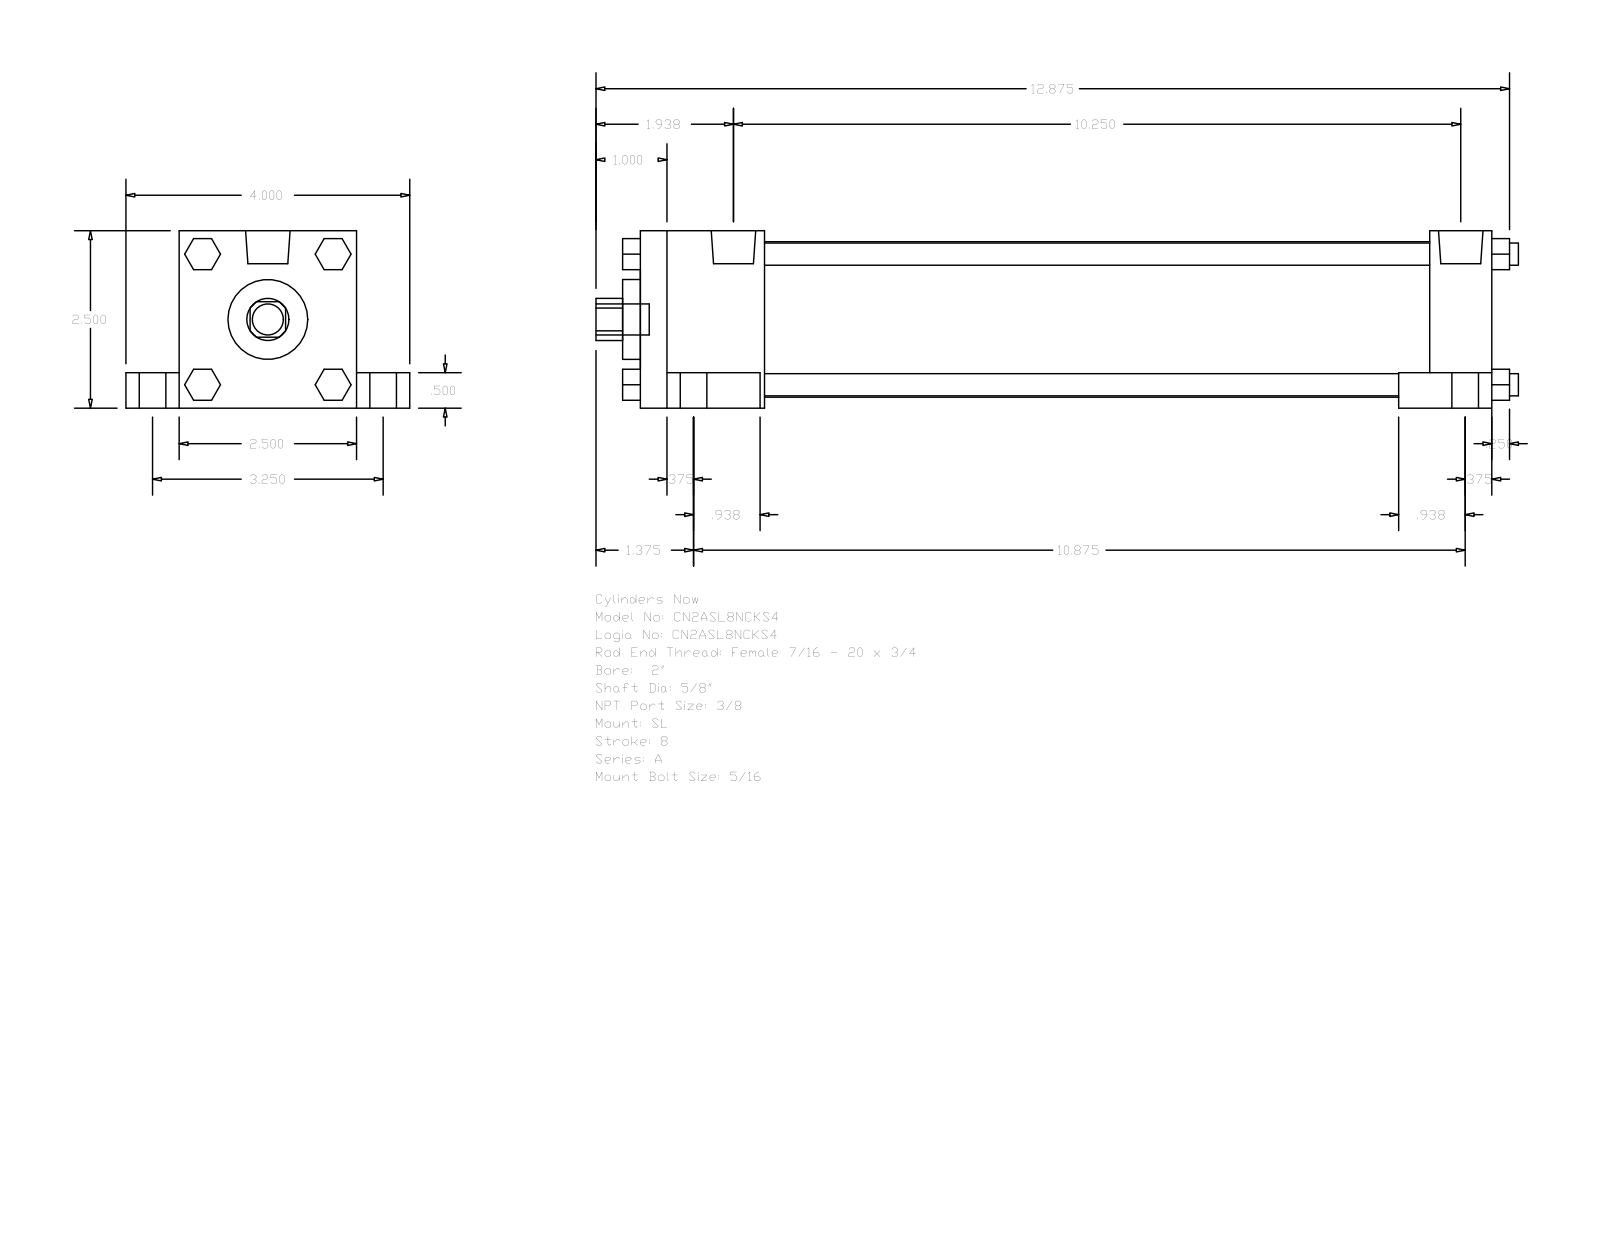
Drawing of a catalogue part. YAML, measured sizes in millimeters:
part_name: "A_SL__0200_0.625"
step_written_by: "GSSL Pune (CONFIG_CONTROL_DESIGN)"
units: millimeters
bodies: {solids: 0, faces: 148, planar: 112, cylindrical: 36, other: 0}
overall_size: [330.2, 101.6, 63.5]
round_holes:
  - {diameter: 15.88, count: 1}
  - {diameter: 28.57, count: 1}
  - {diameter: 55.63, count: 1}
round_bosses_or_shafts:
  - {diameter: 15.88, count: 4}
  - {diameter: 9.53, count: 4}
  - {diameter: 7.94, count: 4}
  - {diameter: 5.56, count: 4}
  - {diameter: 15.93, count: 2}
  - {diameter: 11.11, count: 1}
partial_cylinders:
  - {radius: 7.54, count: 1}
face_to_face_distances: [63.5, 304.8, 50.8, 12.7, 19.05, 82.55, 44.45, 260.35, 282.57, 238.12]
